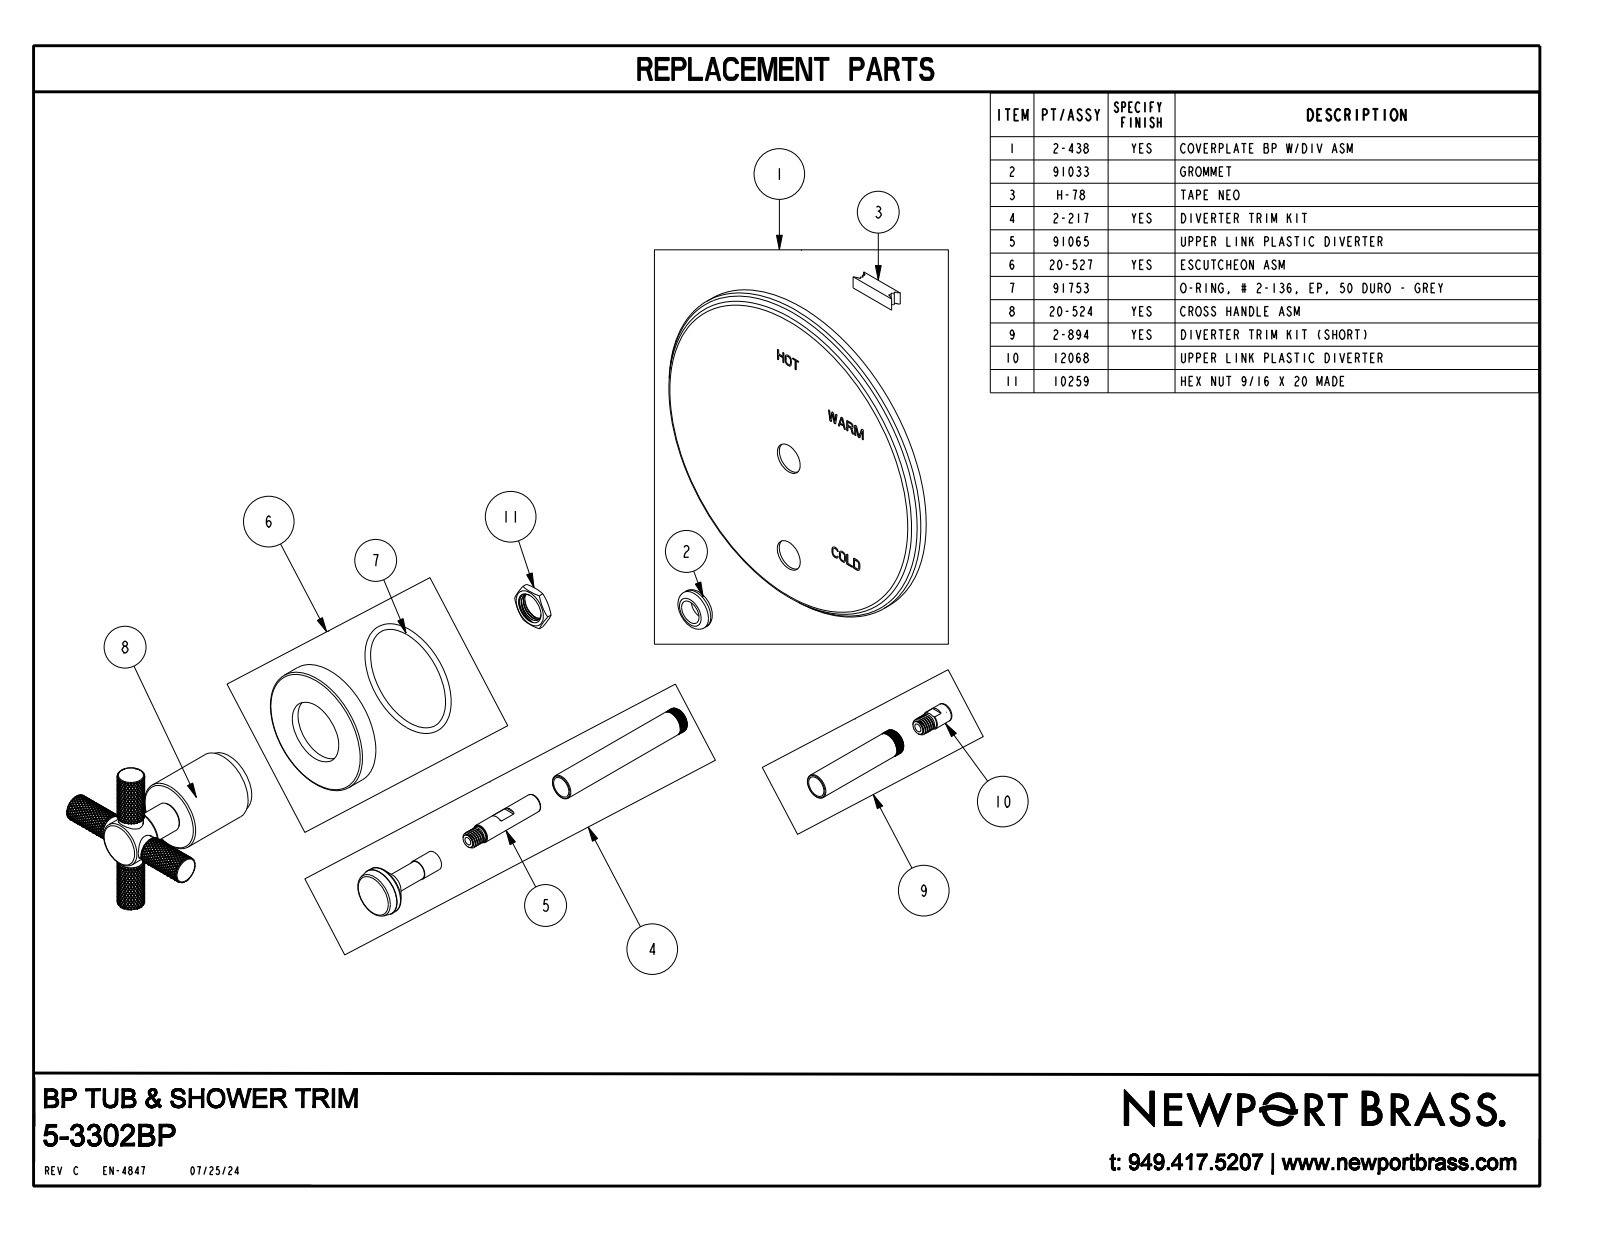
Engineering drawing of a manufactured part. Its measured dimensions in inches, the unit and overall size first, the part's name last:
Units: inches
Overall size (bounding box): 6.5 × 6.5 × 3.379
Round holes (diameter × count): ⌀0.465 ×2, ⌀0.394 ×1
Round bosses / shafts (diameter × count): ⌀0.5 ×2, ⌀0.44 ×2, ⌀6.5 ×1, ⌀2.375 ×1, ⌀1.313 ×1, ⌀1.25 ×1, ⌀0.9 ×1, ⌀0.85 ×1
Main face-to-face distances: 0.313, 0.688, 0.375, 2.088, 1.775, 1.4, 3.379, 3.066, 2.691, 1.291
Volume: 15.33 in³ · Surface area: 95.62 in²
Bodies: 1 solid, 11456 faces (284 planar, 2166 cylindrical, 9006 other)
Part name (STEP PRODUCT): 5-3302BP
STEP written by: CREO PARAMETRIC BY PTC INC, 2018400 (CONFIG_CONTROL_DESIGN)
